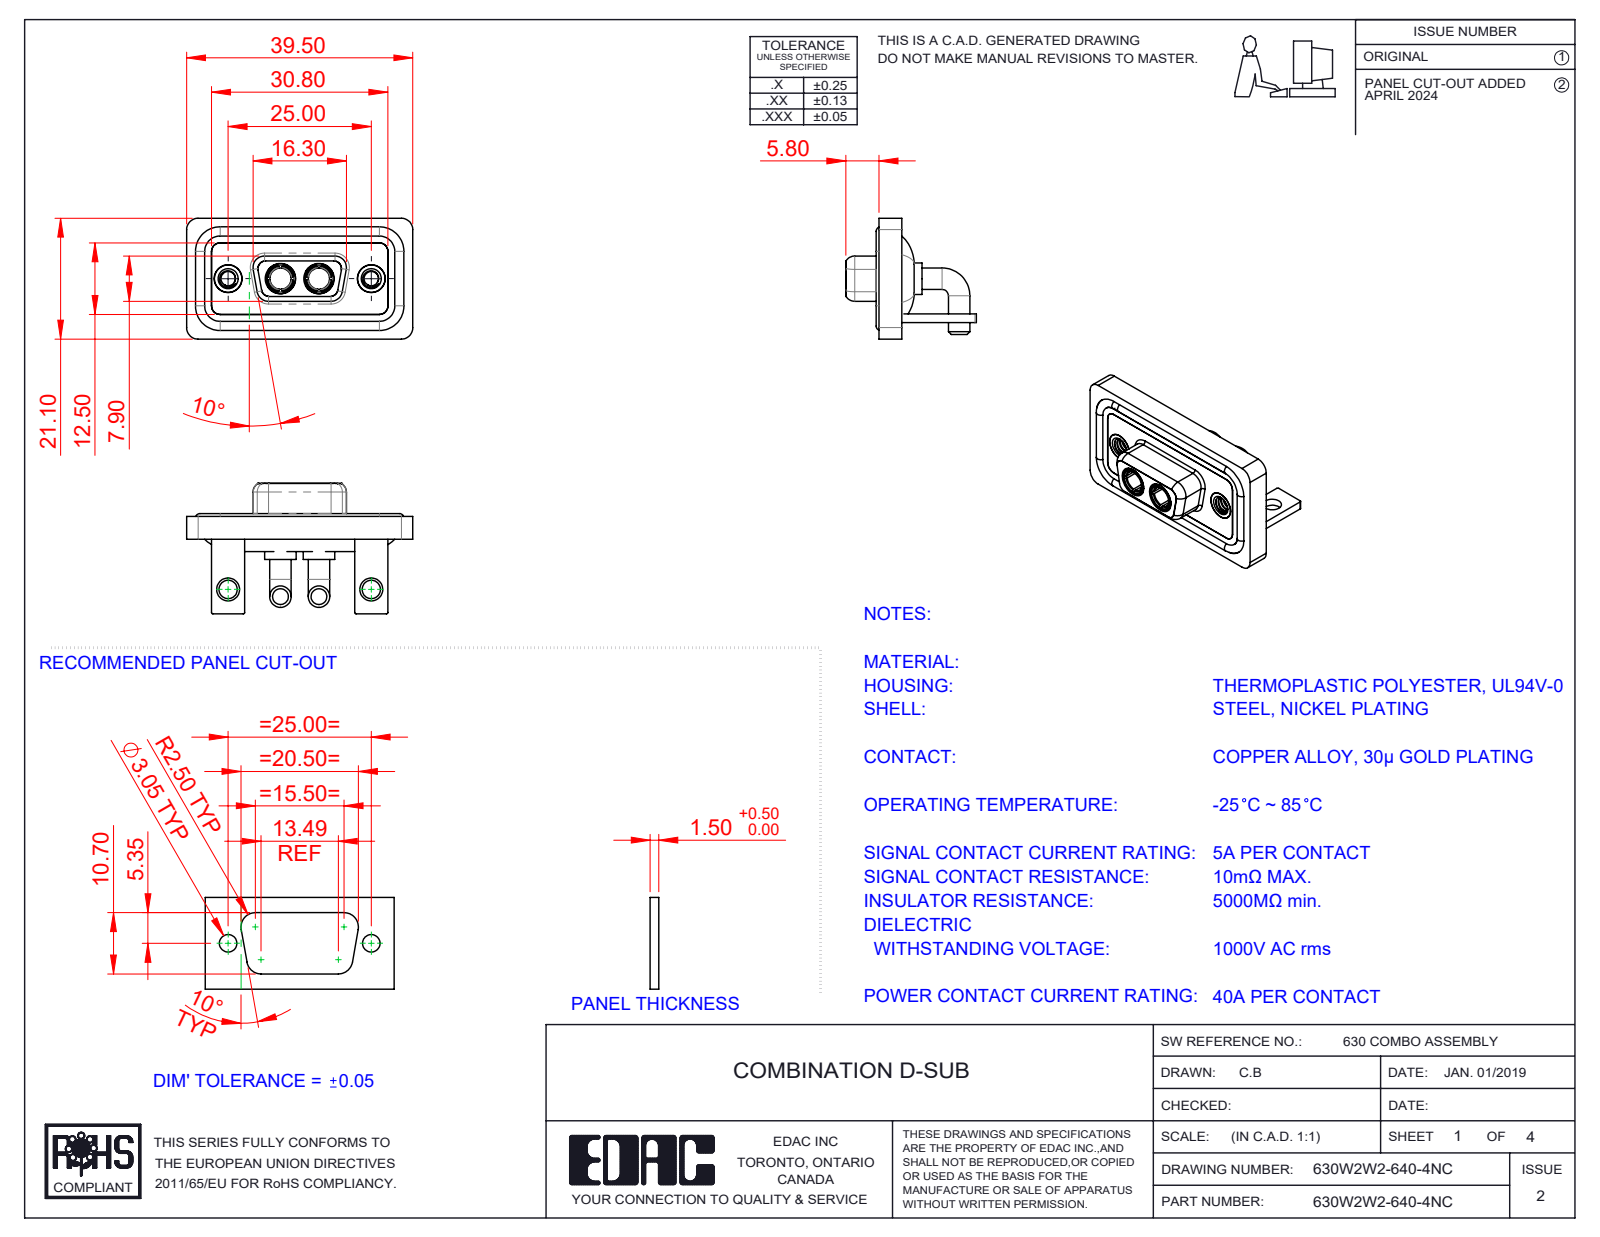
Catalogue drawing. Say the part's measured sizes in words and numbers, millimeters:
The part is named "630Combo Shell Front_09 Contacts; 630Combo Stabilizer Bracket_50 Contacts; 630Combo Waterproof Housing_09 Contacts; 630W2W2-640-4NC (+4 more)". Its 3-D file was written by "SolidWorks 2023 (CONFIG_CONTROL_DESIGN)". It is 13 solids with 584 faces: 183 planar, 260 cylindrical and 141 other. Overall it measures 39.5 by 22.8 by 21.1 millimeters. Its volume is 5 321 cubic millimeters and its surface area 8 612 square millimeters. Round holes: 4 of diameter 4.85, 2 of diameter 2.5, 2 of diameter 3.2, 2 of diameter 3.7, 2 of diameter 4, 2 of diameter 4.05, 2 of diameter 5, 2 of diameter 5.3. Round bosses or shafts: 4 of diameter 3.75, 4 of diameter 1.6, 2 of diameter 5.5, 2 of diameter 5.2, 2 of diameter 4.96, 2 of diameter 4.95, 2 of diameter 4.8, 2 of diameter 4.75. Partial cylindrical surfaces (rounded edges, fillets, slot ends): 19 of radius 2, 18 of radius 1.5, 16 of radius 0.25, 8 of radius 1.35, 8 of radius 1.6, 5 of radius 0.5, 4 of radius 0.6, 4 of radius 0.65. The main face-to-face distances are 0.4, 2.9, 1.5, 1.8, 1.1, 3.7, 0.8, 2.5, 1.6, 3.1. The hole center spacings are 9.14, 15.86, 25, 6.72.
